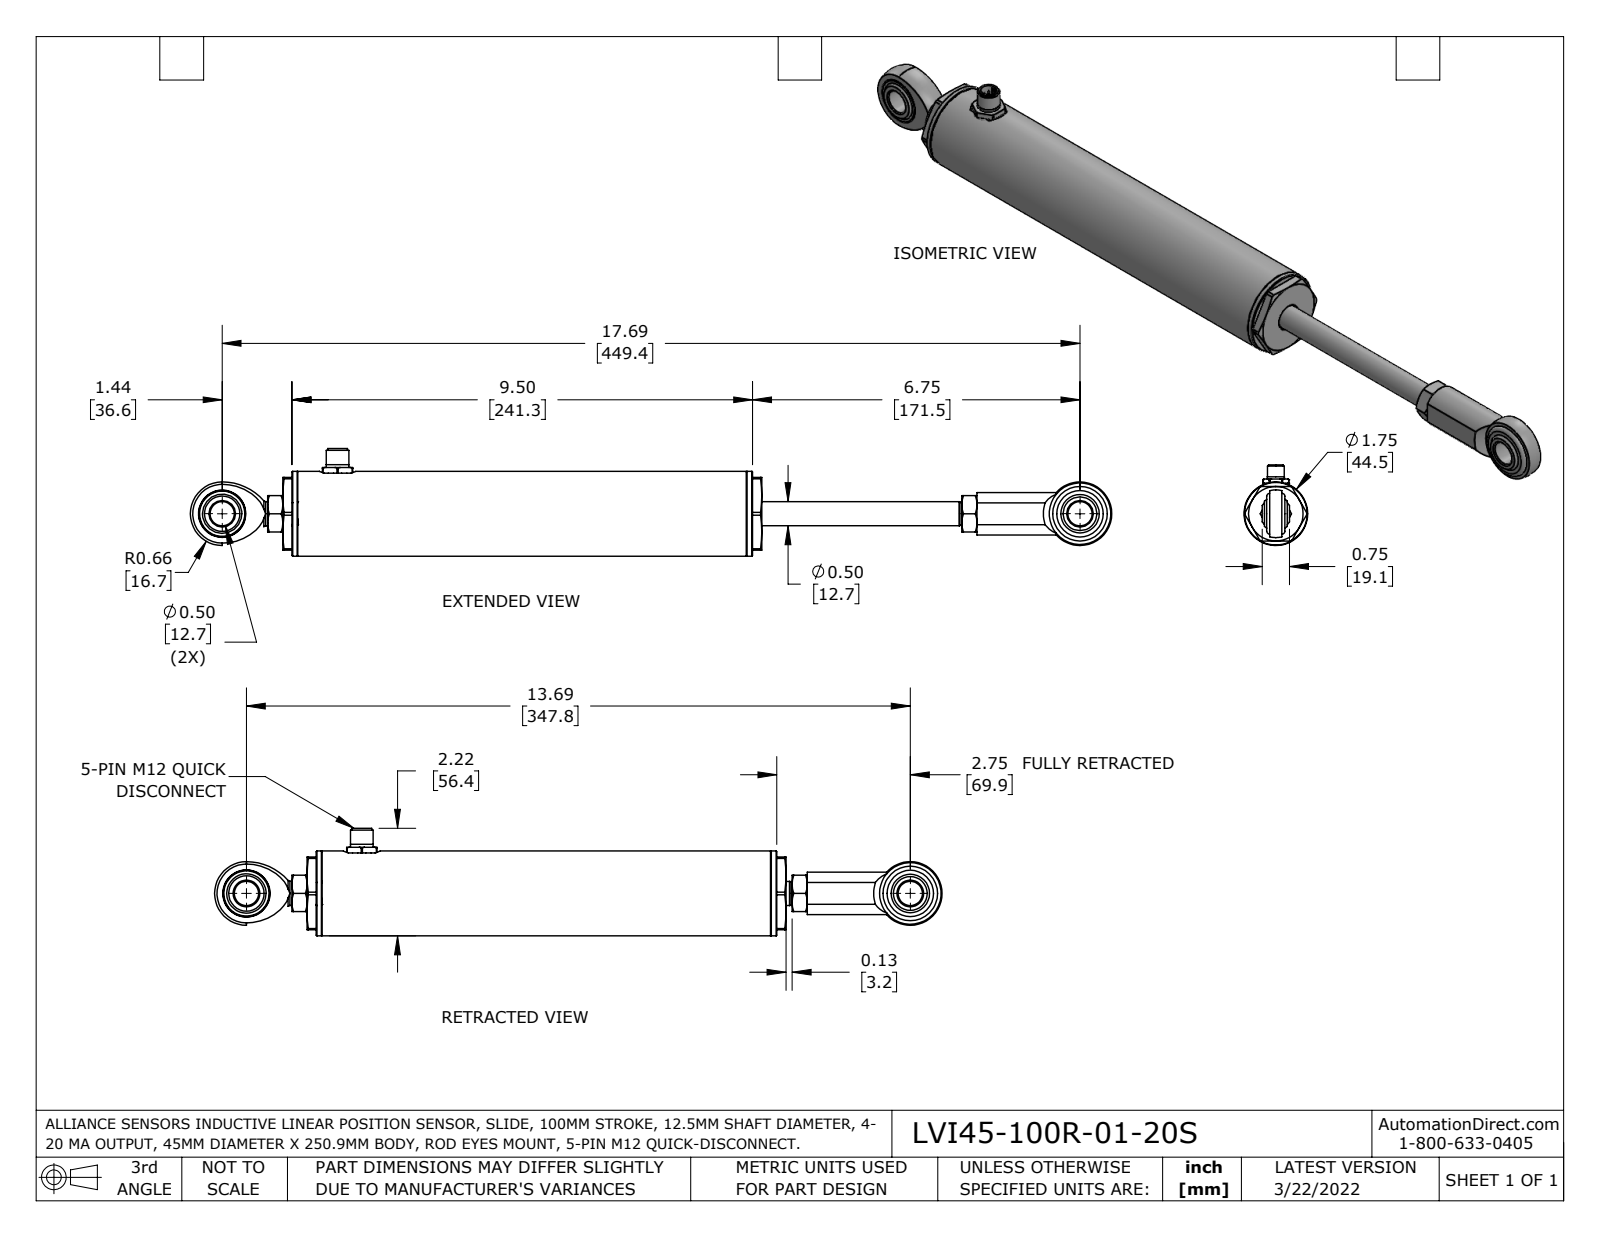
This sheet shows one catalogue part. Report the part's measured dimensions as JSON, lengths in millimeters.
{"part_name": "3100-0024_90025K226; 3900-0015-XX-0_3900-0015-04-0; 3100-0025_9368T161; 3100-0012-YY (+8 more)", "step_written_by": "SolidWorks 2021 (AUTOMOTIVE_DESIGN)", "units": "millimeters", "bodies": {"solids": 23, "faces": 873, "planar": 198, "cylindrical": 297, "other": 378}, "overall_size": [482.7, 56.4, 44.5], "volume_mm3": 232400, "surface_area_mm2": 130300, "round_holes": [[12.7, 3], [5, 1], [6.4, 1], [6.7, 1], [7.8, 1], [8.4, 1], [8.6, 1], [10.5, 1], [10.6, 1], [11.5, 1], [12.1, 1], [12.7, 1]], "round_bosses_or_shafts": [[0.8, 5], [44.5, 1], [41.3, 1], [39.7, 1], [38.9, 1], [38.1, 1], [37.3, 1], [35.2, 1]], "partial_cylinders_radius": [[8.3, 1], [9, 1], [9.6, 1], [9.7, 1], [11.1, 1], [21.6, 1]], "face_to_face_distances": [49, 12.7, 9.7, 17.5, 66.5, 192.4, 56.9, 39.4, 197.2, 179.7], "hole_center_spacings": [12.7, 449.4]}
